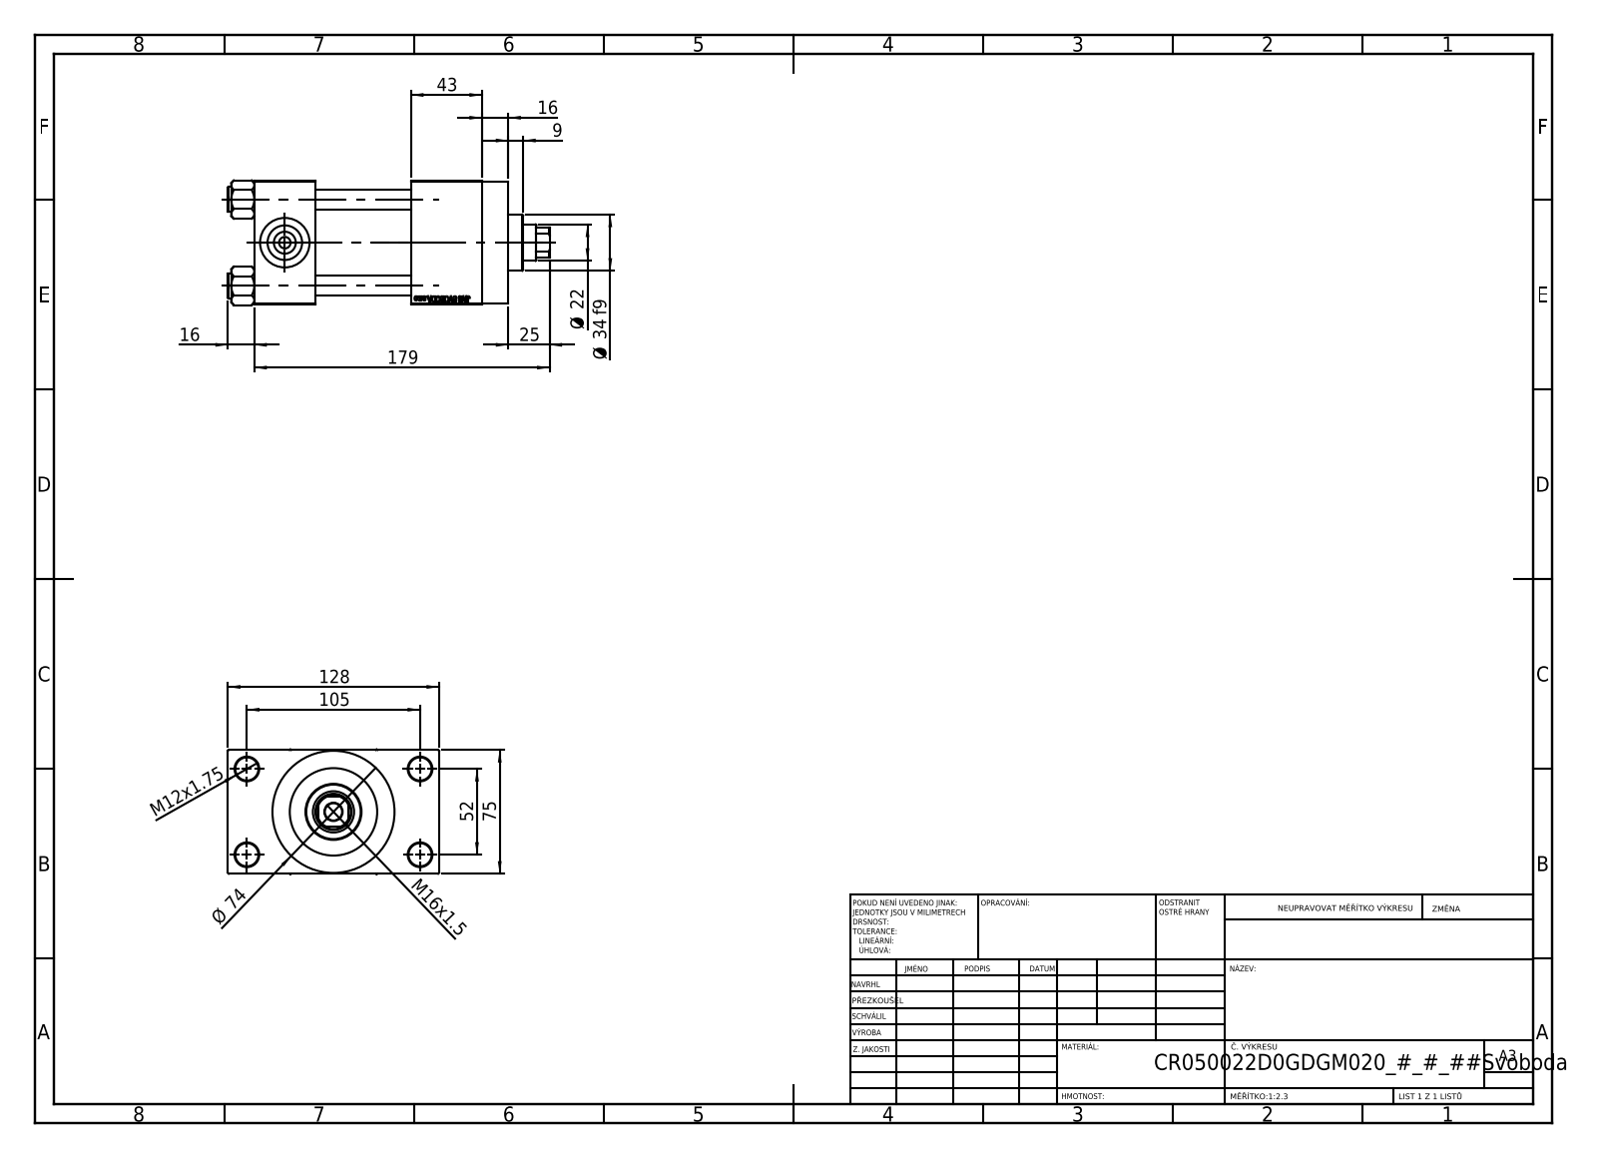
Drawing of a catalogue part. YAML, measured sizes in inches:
part_name: "V215CR_VCP_D; V215CR_D_TYCINKA; V215CR_D_Body; V215_VC_A (+1 more)"
step_written_by: "SolidWorks 2019 (CONFIG_CONTROL_DESIGN)"
units: inches
bodies: {solids: 11, faces: 1103, planar: 497, cylindrical: 88, other: 518}
overall_size: [7.677, 5.039, 2.974]
volume: 49.23
surface_area: 255.7
round_holes:
  - {diameter: 0.472, count: 4}
  - {diameter: 0.551, count: 4}
  - {diameter: 0.276, count: 2}
  - {diameter: 0.825, count: 2}
  - {diameter: 1.181, count: 2}
  - {diameter: 0.413, count: 1}
  - {diameter: 0.866, count: 1}
  - {diameter: 0.984, count: 1}
  - {diameter: 1.614, count: 1}
  - {diameter: 1.969, count: 1}
  - {diameter: 2.087, count: 1}
round_bosses_or_shafts:
  - {diameter: 0.591, count: 4}
  - {diameter: 2.913, count: 1}
  - {diameter: 2.205, count: 1}
  - {diameter: 1.339, count: 1}
partial_cylinders:
  - {radius: 0.413, count: 1}
face_to_face_distances: [2.953, 2.283, 1.457, 3.74, 1.043, 3.996, 5.433, 3.976, 1.693, 0.63]
hole_center_spacings: [1.037, 1.456, 2.059, 2.3, 2.307, 3.096, 3.715, 2.047]
